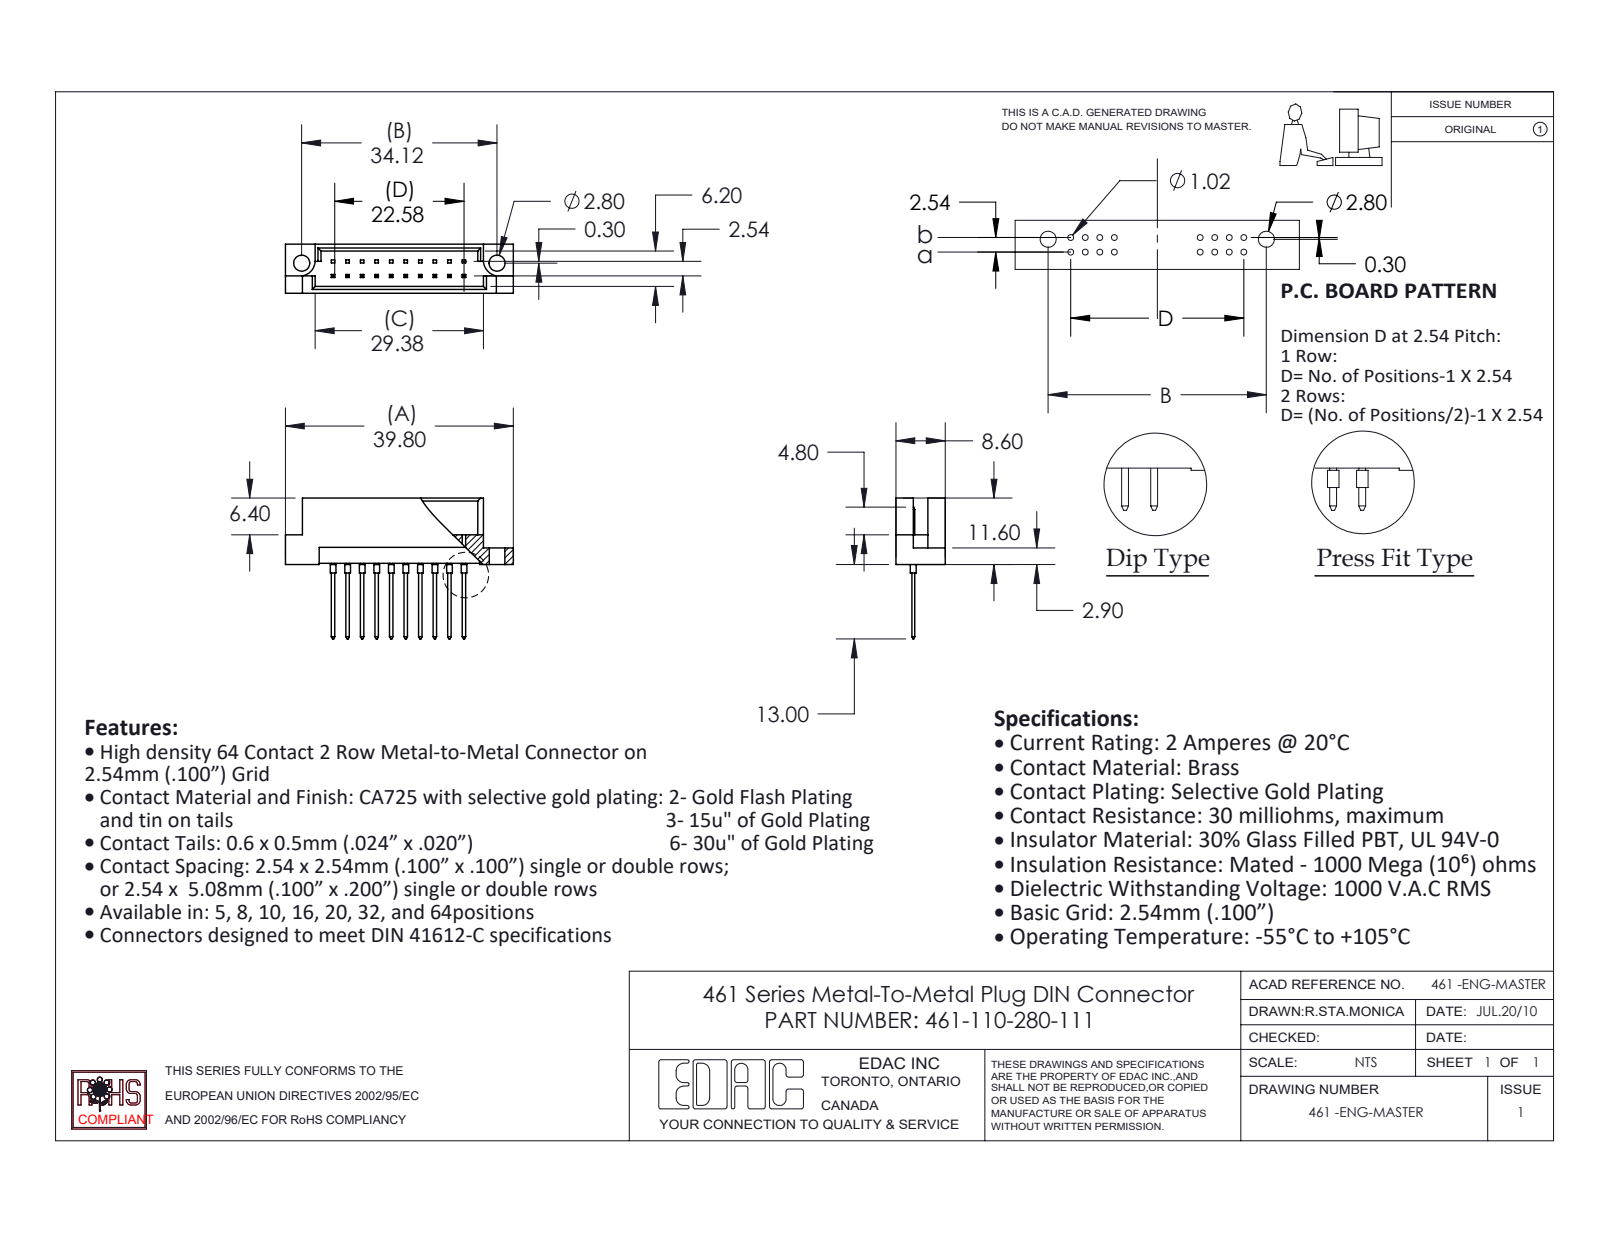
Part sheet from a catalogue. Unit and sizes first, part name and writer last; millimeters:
Units: millimetres
Overall size (bounding box): 39.8 × 24.6 × 8.6
Round holes (diameter × count): ⌀2.8 ×2
Round bosses / shafts (diameter × count): ⌀1 ×10
Partial cylindrical surfaces — rounded edges, fillets, slot ends (radius × count): R2.8 ×2
Main face-to-face distances: 1.2, 7.4, 8.6, 2.54, 6.2, 3.28, 5.32, 2.08, 4.12, 2.78
Hole centre spacings: 34.12
Volume: 1 980 mm³ · Surface area: 2 864 mm²
Bodies: 11 solids, 348 faces (322 planar, 26 cylindrical, 0 other)
Part name (STEP PRODUCT): 461-290_80; 461-110-280-111; 461 Part_20
STEP written by: SolidWorks 2020 (CONFIG_CONTROL_DESIGN)
